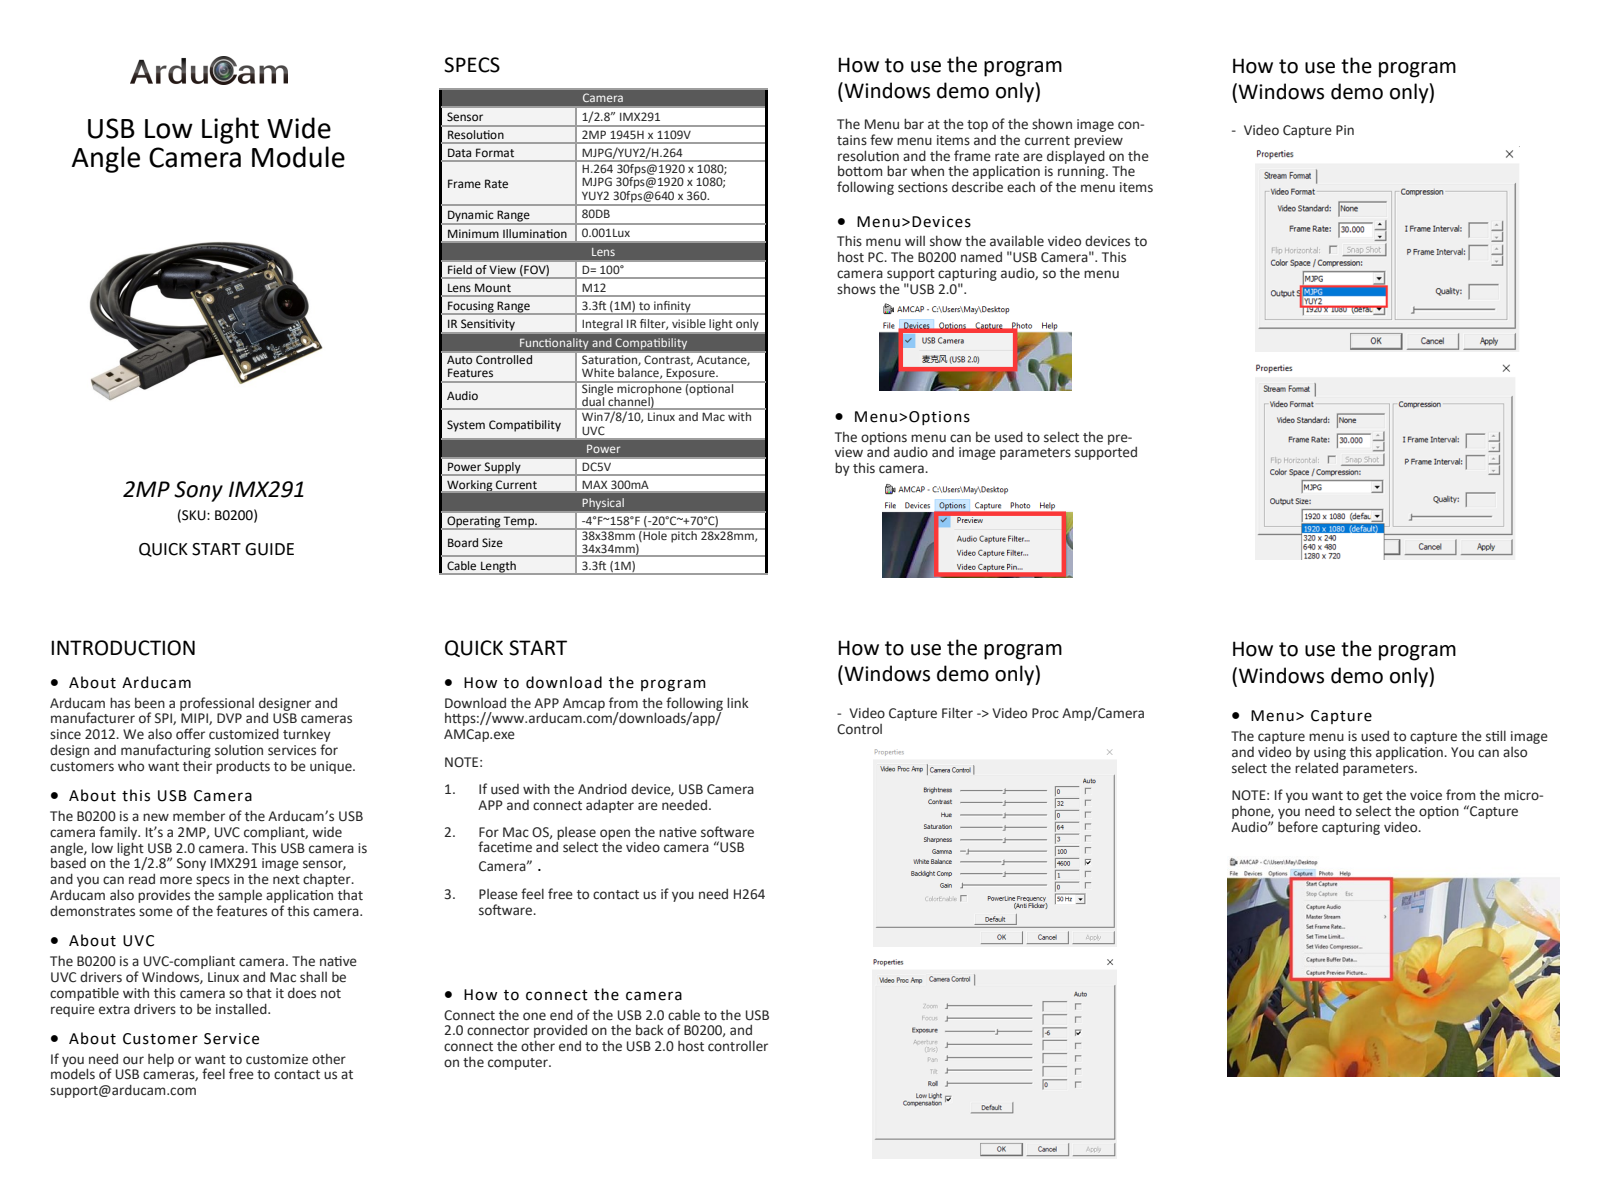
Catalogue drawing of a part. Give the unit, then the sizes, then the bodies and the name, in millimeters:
Units: millimetres
Overall size (bounding box): 39.42 × 39.42 × 27.1
Round holes (diameter × count): ⌀2.5 ×4, ⌀1.5 ×2, ⌀5 ×1, ⌀11.38 ×1, ⌀12 ×1, ⌀14 ×1
Round bosses / shafts (diameter × count): ⌀0.5 ×4, ⌀17 ×1, ⌀12.1 ×1, ⌀9 ×1
Partial cylindrical surfaces — rounded edges, fillets, slot ends (radius × count): R0.48 ×42, R0.15 ×40, R1.81 ×8, R1.25 ×4, R8.9 ×4, R2 ×2, R6.7 ×1
Main face-to-face distances: 1.1, 3.5, 13, 0.55, 14.55, 0.5, 12.16, 12.71, 26.71, 27.26
Hole centre spacings: 9, 14.43, 14.6, 19.32, 19.66, 26.46, 26.87, 27.32
Volume: 4 431 mm³ · Surface area: 8 482 mm²
Bodies: 11 solids, 749 faces (223 planar, 357 cylindrical, 169 other)
Part name (STEP PRODUCT): B0200
STEP written by: SolidWorks 2018 (AUTOMOTIVE_DESIGN)
